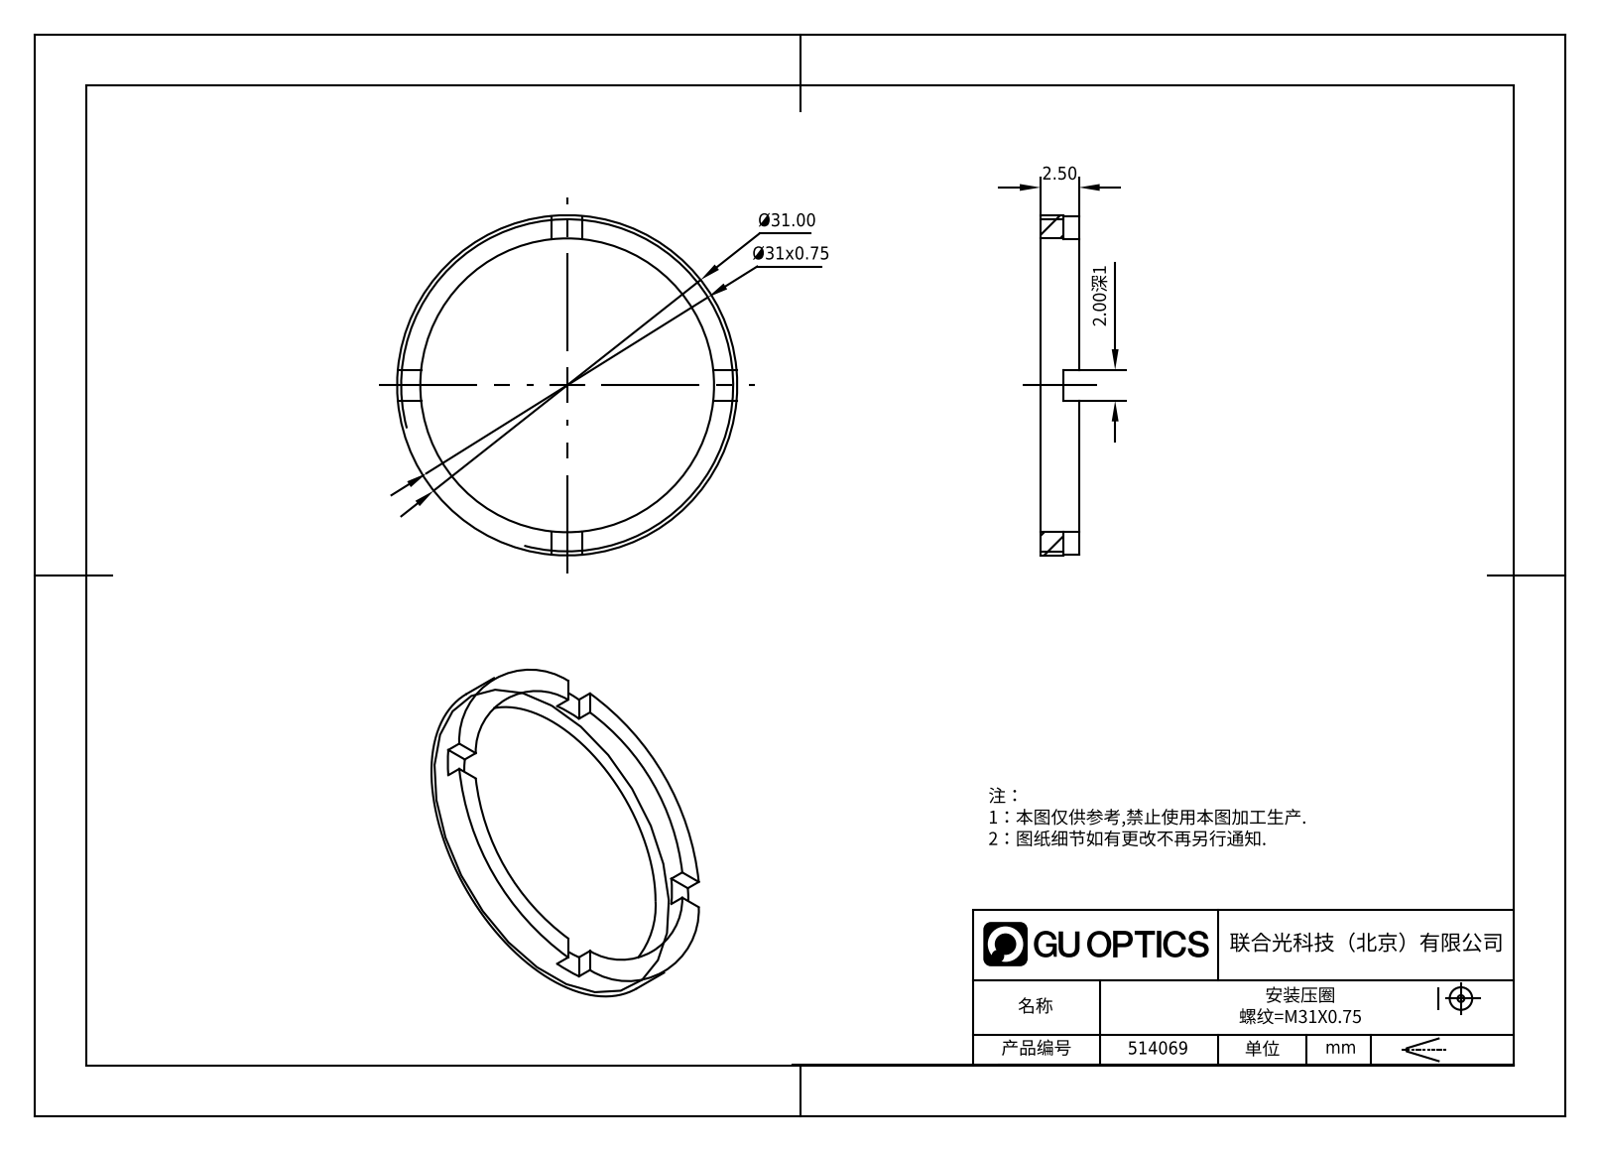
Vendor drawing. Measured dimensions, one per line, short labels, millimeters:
name: 514069
written by: SolidWorks 2020 (CONFIG_CONTROL_DESIGN)
unit: mm
bodies: 1 solid, 21 faces (17 planar, 4 cylindrical, 0 other)
size: 31 × 31 × 2.5
volume: 440 mm³; area: 820 mm²
holes: 1× ⌀27
bosses: 1× ⌀31
face distances: 2.5, 1.5, 1, 2
